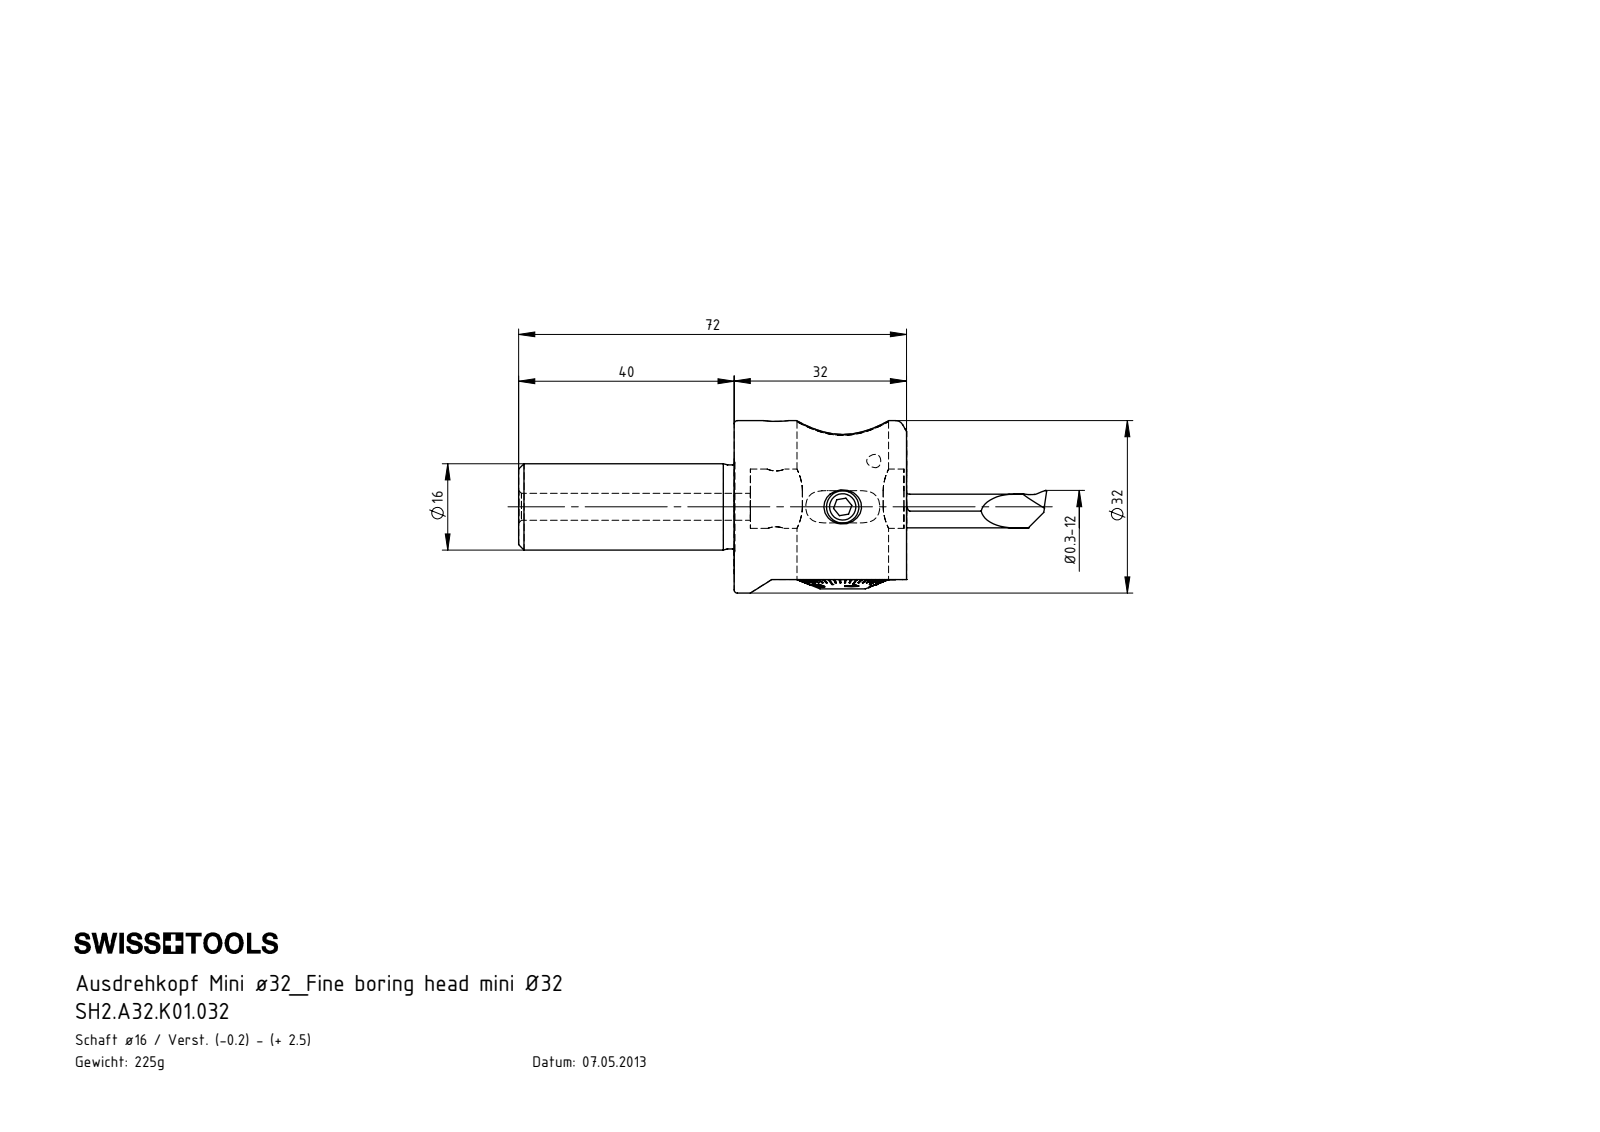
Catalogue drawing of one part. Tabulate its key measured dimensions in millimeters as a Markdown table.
| quantity | value |
| --- | --- |
| part name | ISO 4026 - M6 x 10; A32-BG1.012.017; A32-BG2.014.010_A; Klebstoff D6 (+8 more) |
| STEP written by | SolidWorks 2017 (AUTOMOTIVE_DESIGN) |
| units | millimeters |
| bodies | 15 solids, 715 faces (302 planar, 137 cylindrical, 276 other) |
| overall size | 72 × 32 × 32 |
| volume | 29 075 mm³ |
| surface area | 15 807 mm² |
| round holes (diameter × count) | 5 × 8, 3.3 × 2, 1 × 1, 2 × 1, 2.5 × 1, 2.9 × 1, 3 × 1, 6 × 1, 7 × 1, 7.75 × 1, 8.4 × 1, 10.2 × 1 |
| round bosses / shafts (diameter × count) | 6 × 3, 32 × 1, 17 × 1, 16.98 × 1, 16.85 × 1, 16 × 1, 15.6 × 1, 14.65 × 1 |
| partial cylindrical surfaces (radius × count) | 0.21 × 6, 0.36 × 5, 0.2 × 4, 2.2 × 4, 4 × 2, 0.36 × 1, 0.5 × 1, 1.9 × 1 |
| main face-to-face distances | 32, 4.5, 3.7, 0.8, 1.5, 2.3, 2.2, 3, 40, 72 |
| hole center spacings | 4.5, 10.4, 11.88, 12.21, 0.4, 7.9, 8, 8.01 |
